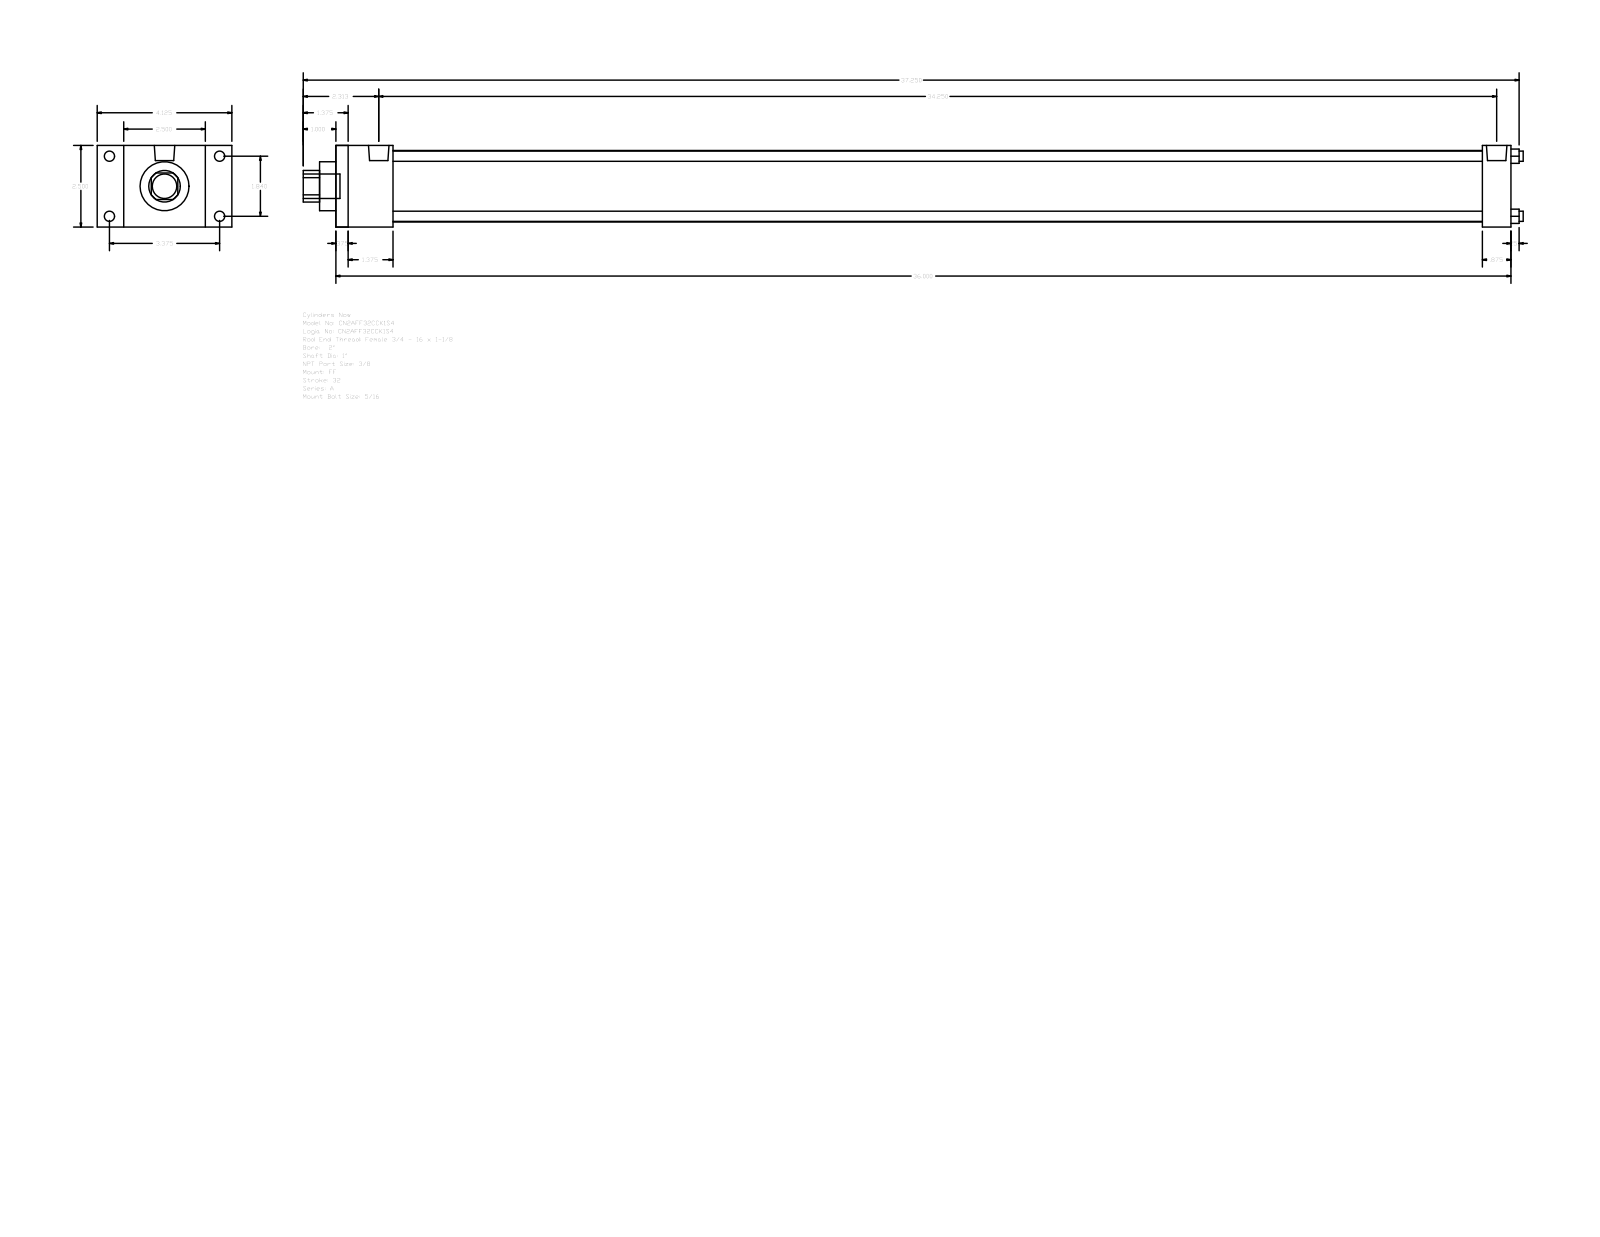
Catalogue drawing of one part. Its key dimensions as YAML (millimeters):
part_name: "A_FF__0200_1"
step_written_by: "GSSL Pune (CONFIG_CONTROL_DESIGN)"
units: millimeters
bodies: {solids: 0, faces: 92, planar: 64, cylindrical: 28, other: 0}
overall_size: [949.33, 104.78, 63.5]
round_holes:
  - {diameter: 7.94, count: 4}
  - {diameter: 25.4, count: 1}
  - {diameter: 38.1, count: 1}
  - {diameter: 55.63, count: 1}
round_bosses_or_shafts:
  - {diameter: 7.94, count: 4}
  - {diameter: 5.56, count: 4}
  - {diameter: 15.93, count: 2}
  - {diameter: 19.05, count: 1}
partial_cylinders:
  - {radius: 12.29, count: 1}
face_to_face_distances: [63.5, 914.4, 904.88, 9.52, 22.22, 20.64, 44.45, 892.18, 34.93, 882.66]
hole_center_spacings: [33.05, 46.74, 66.1]
